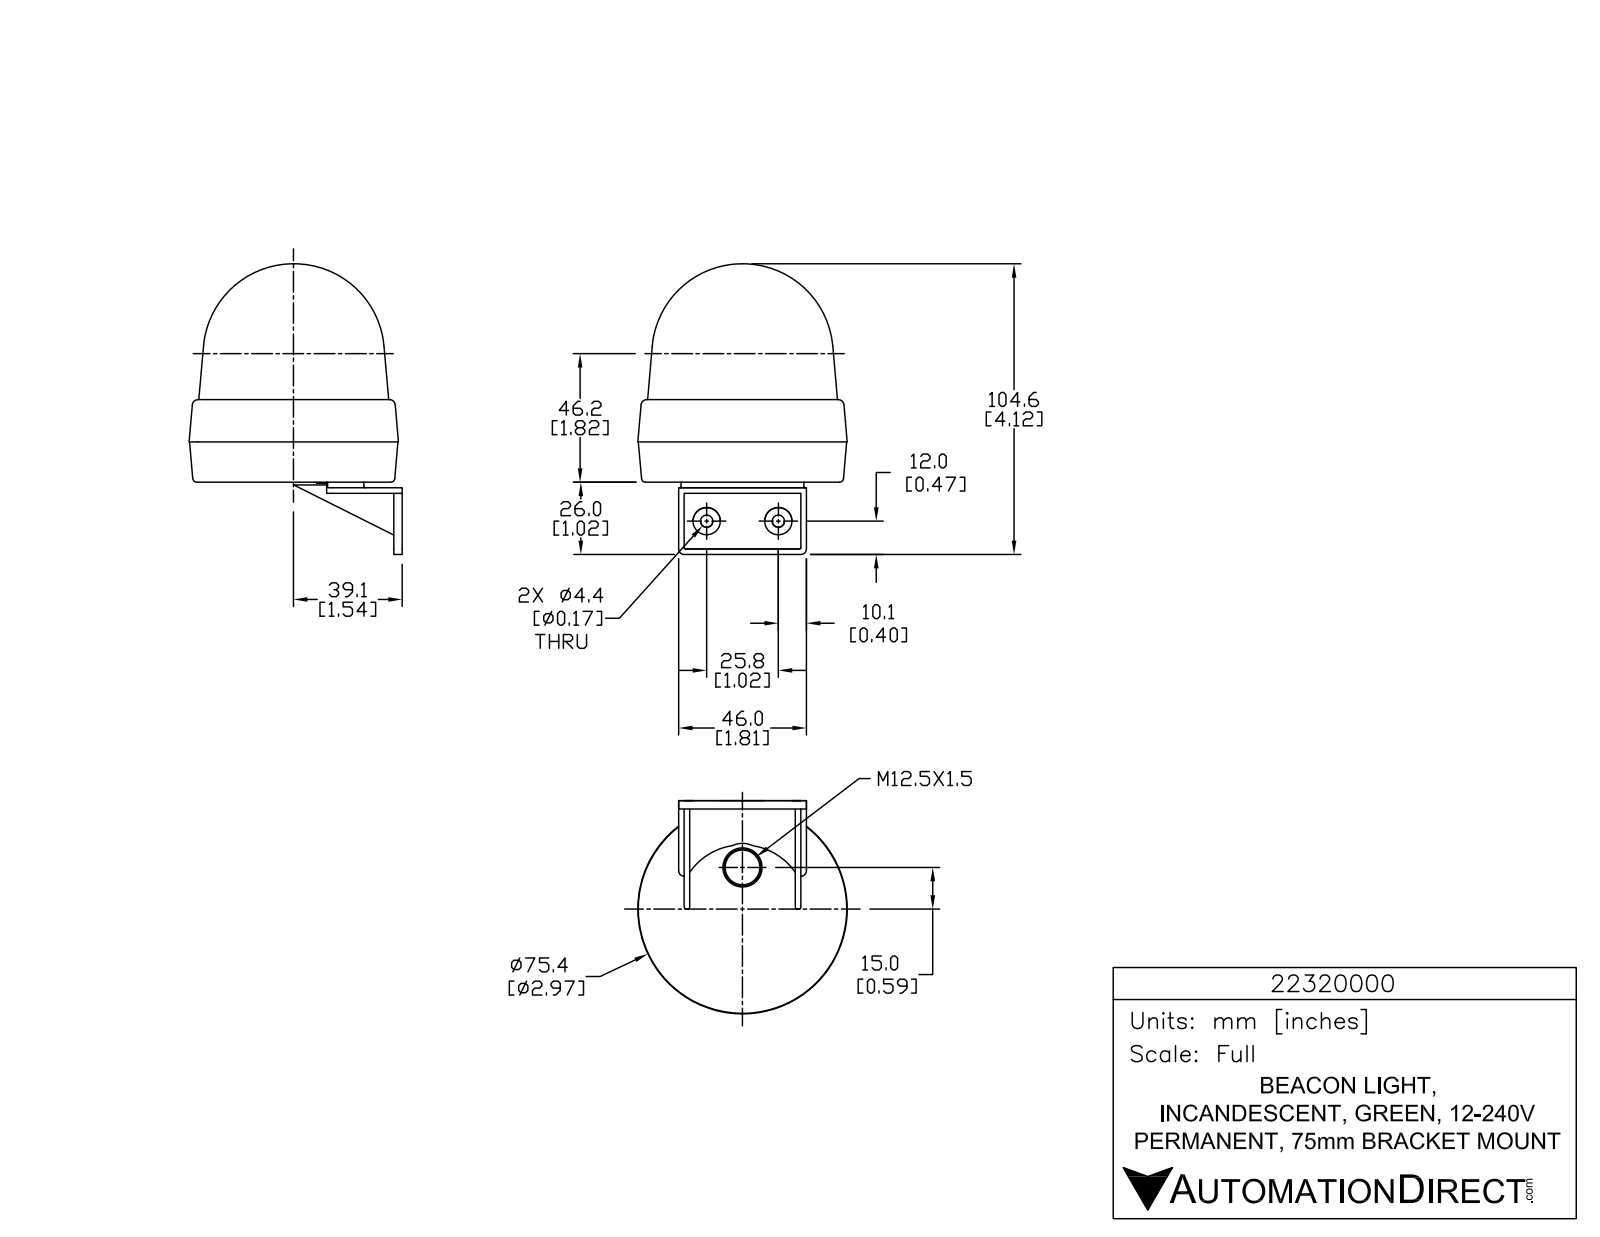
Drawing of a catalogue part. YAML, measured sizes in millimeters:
part_name: "22320000"
step_written_by: "SolidWorks 2015 (AUTOMOTIVE_DESIGN)"
units: millimeters
bodies: {solids: 1, faces: 819, planar: 549, cylindrical: 180, other: 90}
overall_size: [104.6, 82.6, 75.4]
volume: 262500
surface_area: 27080
round_holes:
  - {diameter: 1.5, count: 3}
  - {diameter: 4.4, count: 2}
round_bosses_or_shafts:
  - {diameter: 8.6, count: 3}
  - {diameter: 2.1, count: 3}
  - {diameter: 9.8, count: 2}
partial_cylinders:
  - {radius: 0.1, count: 9}
  - {radius: 0.1, count: 6}
  - {radius: 0.3, count: 6}
  - {radius: 0.3, count: 6}
  - {radius: 0.3, count: 6}
  - {radius: 0.5, count: 6}
  - {radius: 5, count: 6}
  - {radius: 2, count: 4}
face_to_face_distances: [2, 4, 40, 1, 3, 42, 38, 2, 42, 44]
hole_center_spacings: [25.8]
